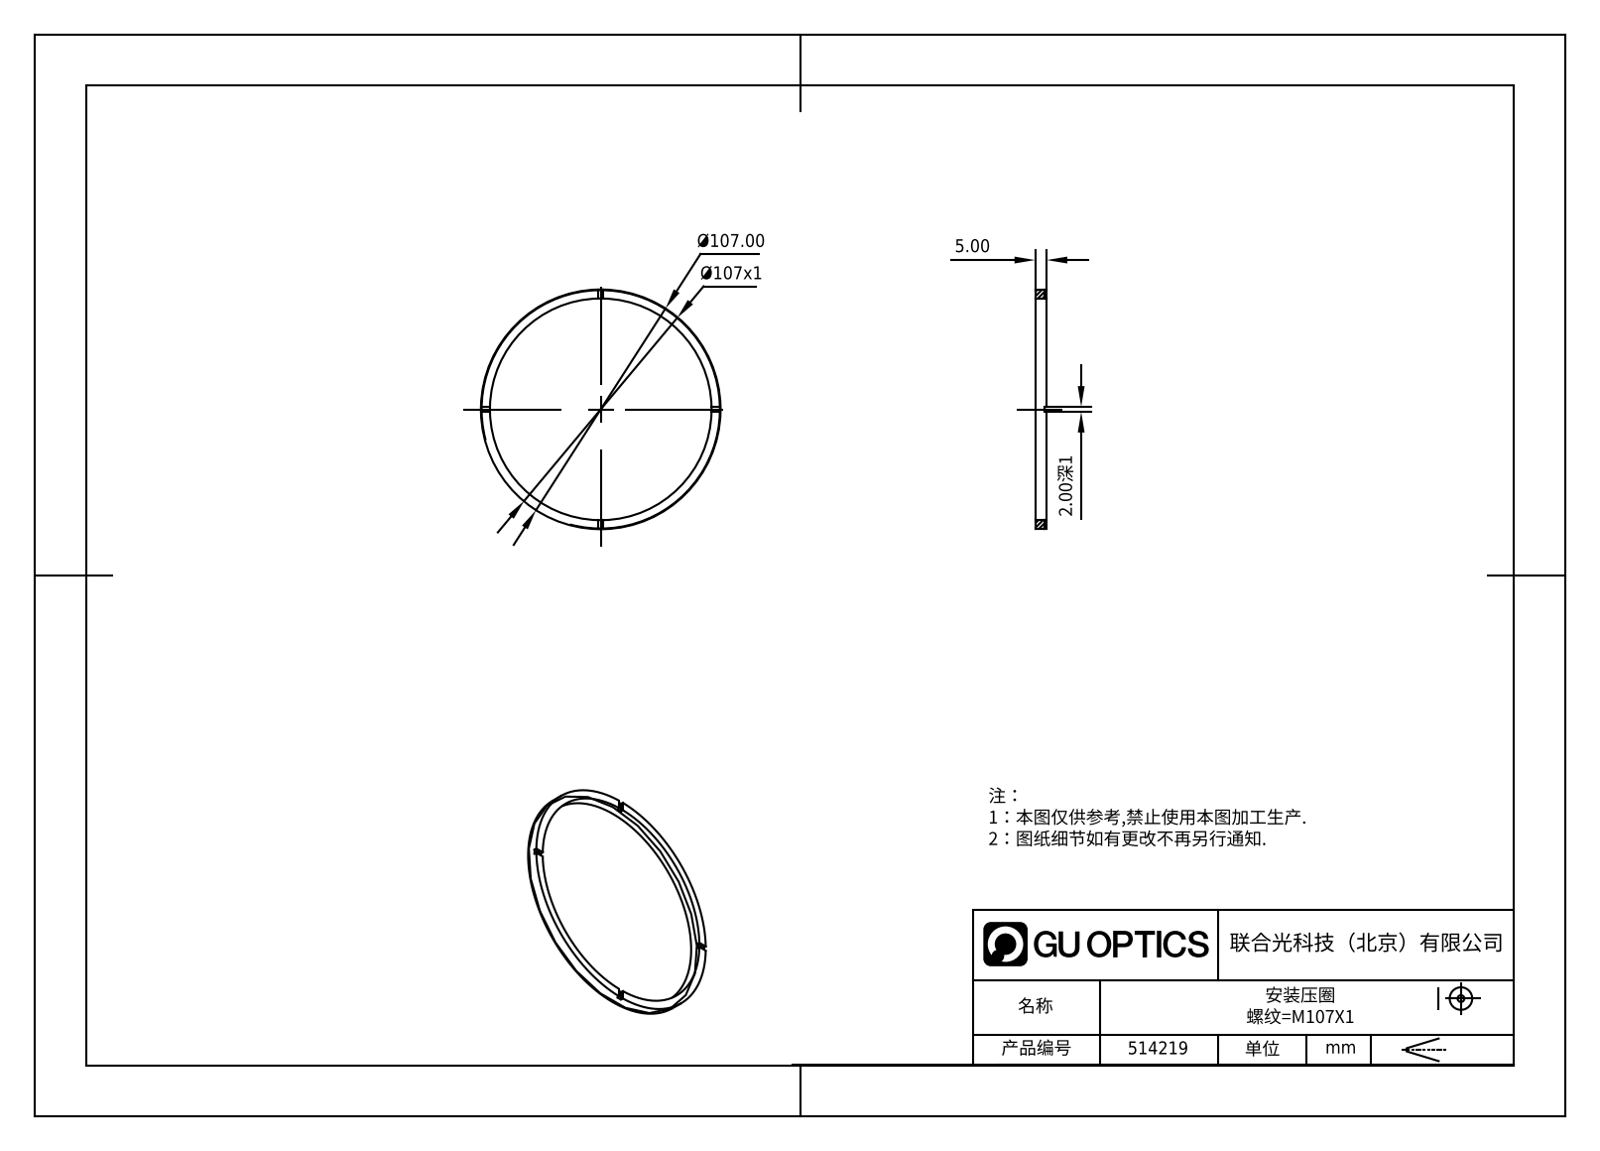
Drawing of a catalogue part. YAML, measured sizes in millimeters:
part_name: "514219"
step_written_by: "SolidWorks 2020 (CONFIG_CONTROL_DESIGN)"
units: millimeters
bodies: {solids: 1, faces: 21, planar: 17, cylindrical: 4, other: 0}
overall_size: [107, 107, 5]
volume: 6440
surface_area: 5841
round_holes:
  - {diameter: 99, count: 1}
round_bosses_or_shafts:
  - {diameter: 107, count: 1}
face_to_face_distances: [5, 4, 1, 2]
